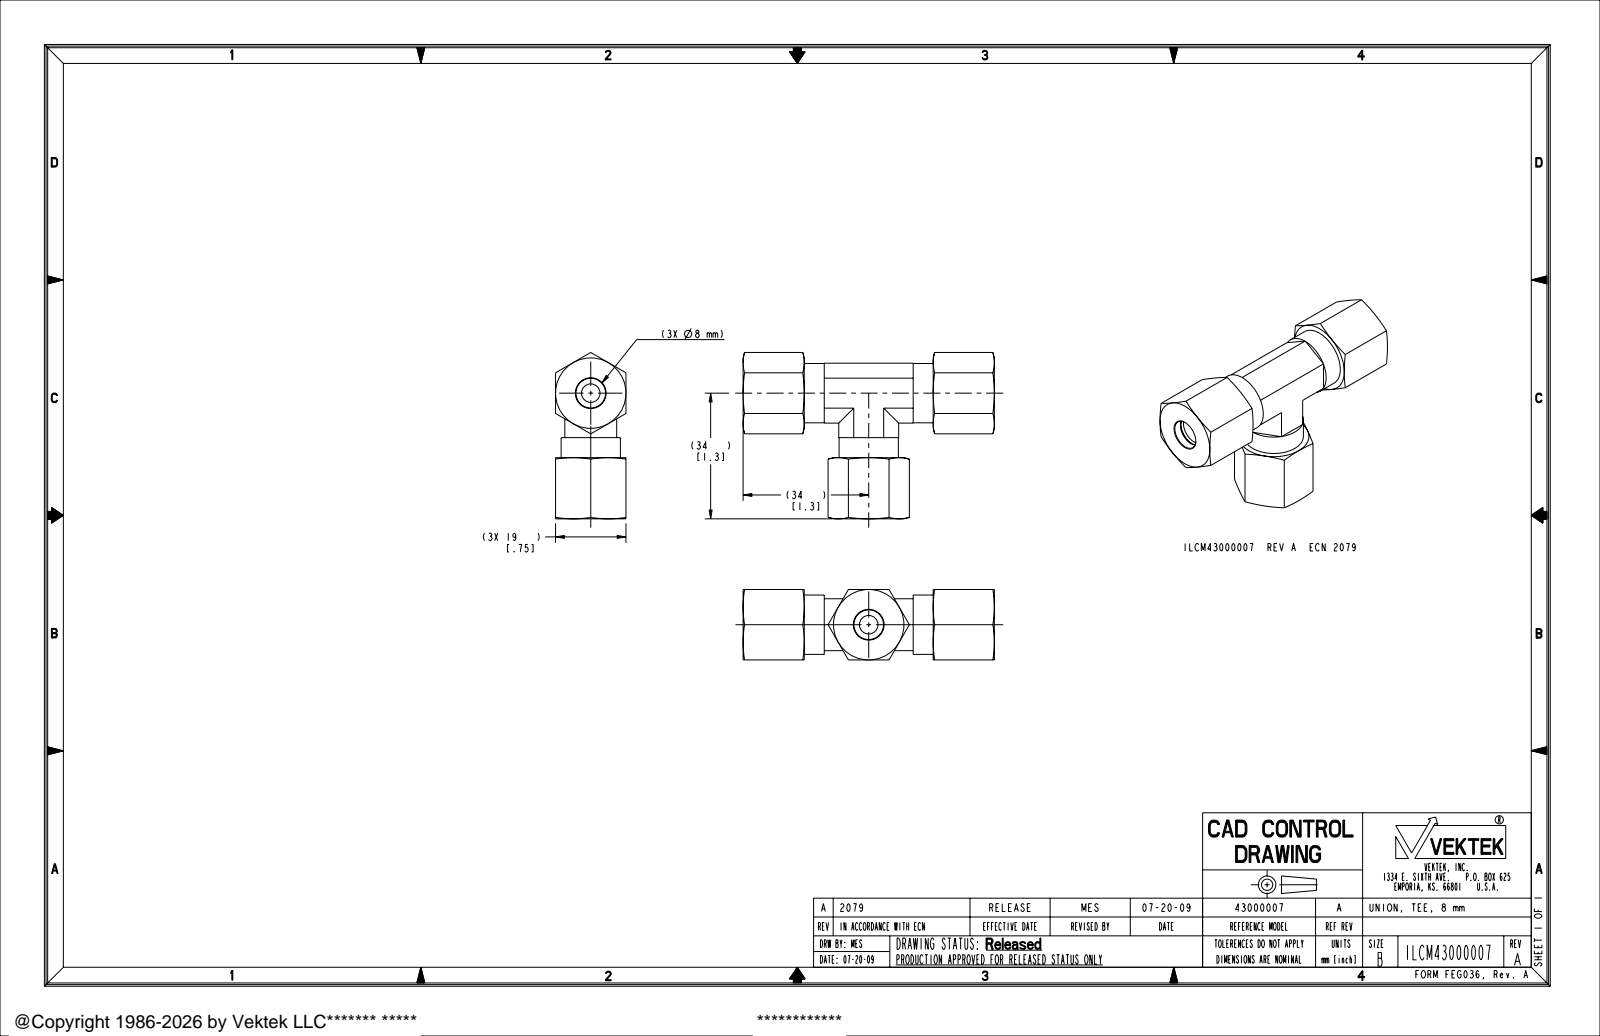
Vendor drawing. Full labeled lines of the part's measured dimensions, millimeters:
Part name (STEP PRODUCT): ILCM43000007
STEP written by: PRO/ENGINEER BY PARAMETRIC TECHNOLOGY CORPORATION, 2007460 (AUTOMOTIVE_DESIGN_CC2)
Units: millimetres
Bodies: 1 solid, 217 faces (87 planar, 46 cylindrical, 84 other)
Overall size (bounding box): 67.8 × 44.9 × 19
Volume: 18 980 mm³ · Surface area: 10 550 mm²
Round holes (diameter × count): ⌀5 ×2, ⌀8 ×2, ⌀14.4 ×2
Round bosses / shafts (diameter × count): ⌀16 ×2, ⌀11 ×2, ⌀10.1 ×2
Main face-to-face distances: 19, 16.5, 2.5, 14, 67.8, 9.9, 6.6, 51.3, 57.9, 41.4
